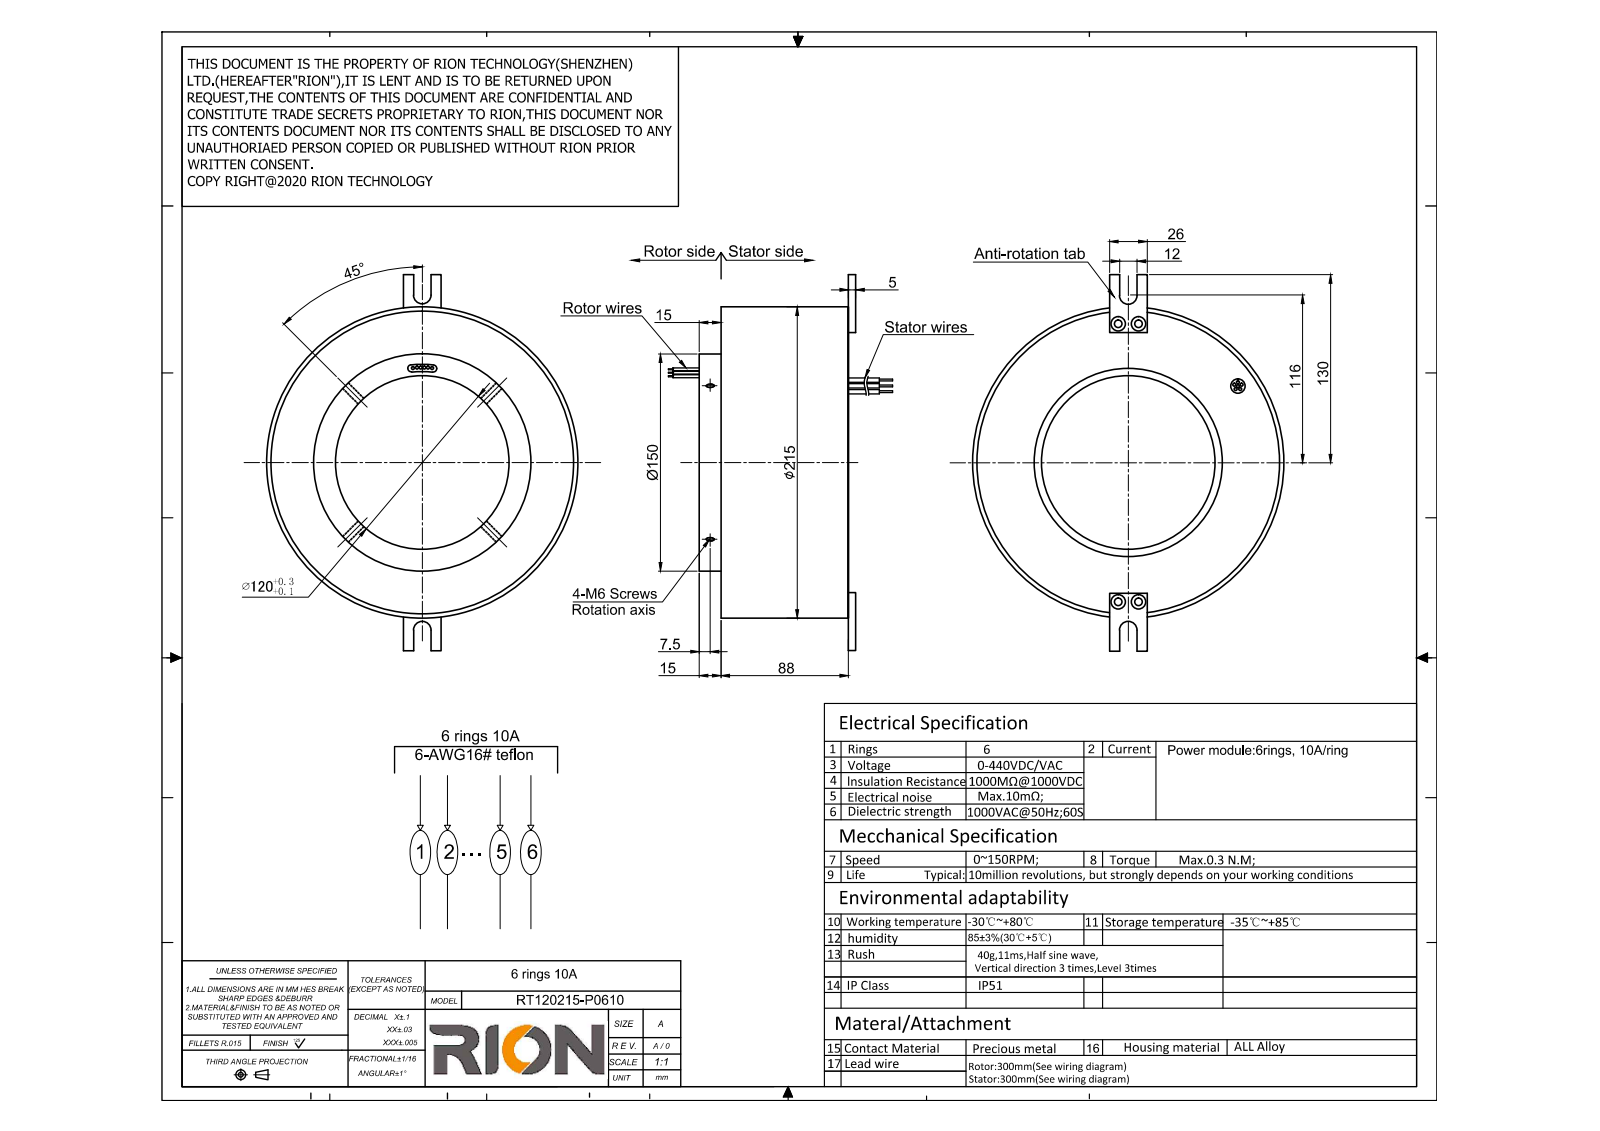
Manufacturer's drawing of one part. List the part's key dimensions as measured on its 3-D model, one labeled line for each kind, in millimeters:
Part name (STEP PRODUCT): MT120215-P0610
STEP written by: SolidWorks 2014 (CONFIG_CONTROL_DESIGN)
Units: millimetres
Bodies: 1 solid, 140 faces (48 planar, 76 cylindrical, 16 other)
Overall size (bounding box): 260 × 215 × 190
Volume: 2 302 000 mm³ · Surface area: 178 496 mm²
Round holes (diameter × count): ⌀5 ×8, ⌀4.2 ×4, ⌀10 ×1, ⌀120 ×1, ⌀130.2 ×1, ⌀209.2 ×1
Round bosses / shafts (diameter × count): ⌀2.1 ×12, ⌀215 ×1, ⌀209 ×1, ⌀150 ×1, ⌀130 ×1
Partial cylindrical surfaces — rounded edges, fillets, slot ends (radius × count): R2.5 ×2, R6 ×2, R63 ×1, R68 ×1
Main face-to-face distances: 88, 15, 103, 5, 108, 93, 26, 7, 19, 40
Hole centre spacings: 96.25, 14, 192, 192.51, 81.08, 92.5, 93.25, 164.16
